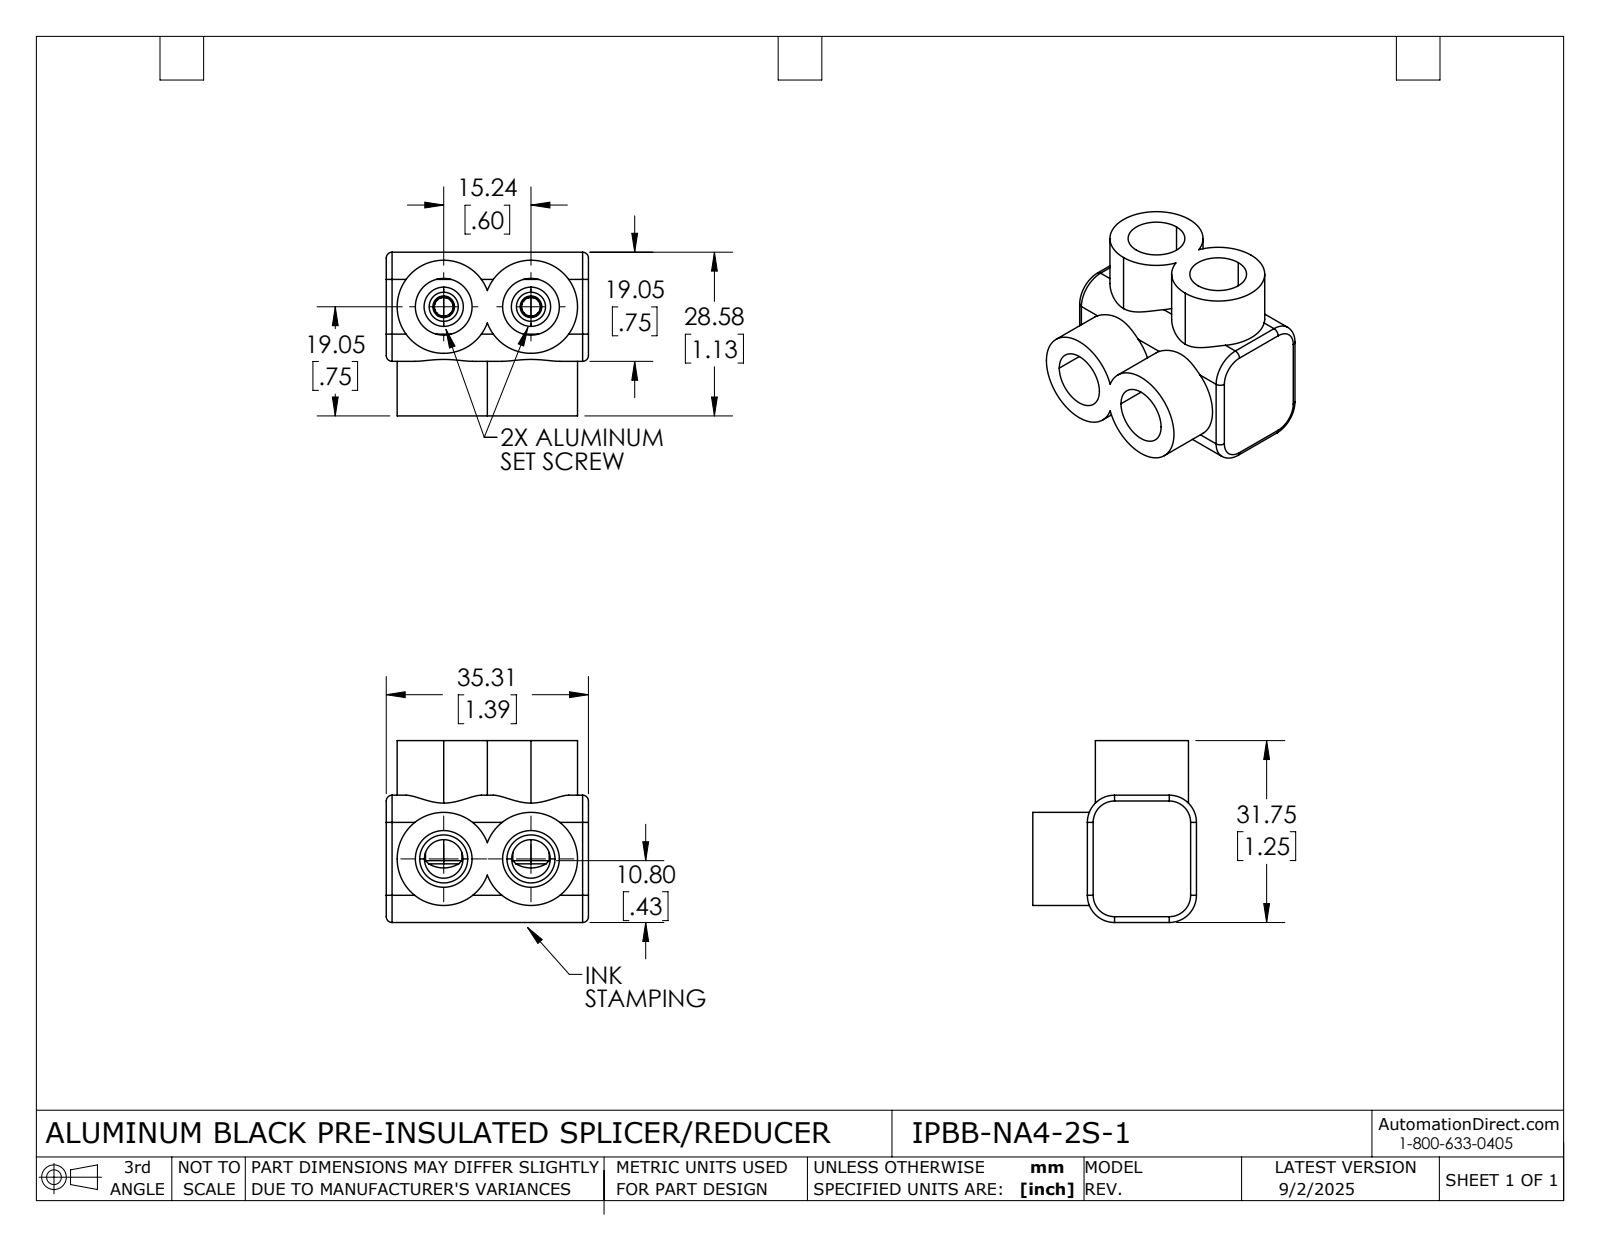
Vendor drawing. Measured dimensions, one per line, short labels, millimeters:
name: IPBB-NA4-2S-1
written by: SolidWorks 2024 (AUTOMOTIVE_DESIGN)
unit: mm
bodies: 4 solids, 167 faces (70 planar, 57 cylindrical, 40 other)
size: 35.3 × 31.8 × 28.6
volume: 17 450 mm³; area: 11 080 mm²
holes: 4× ⌀9.9, 2× ⌀3.3, 2× ⌀5.4, 2× ⌀6.7
bosses: 4× ⌀16.3, 2× ⌀6.4
rounds: 8× R1, 4× R1.6, 4× R4.7
face distances: 3.2, 12.7, 15.9, 32.1, 28.6, 3.2, 29, 19.1, 35.3, 31.8
hole spacings: 15.2
